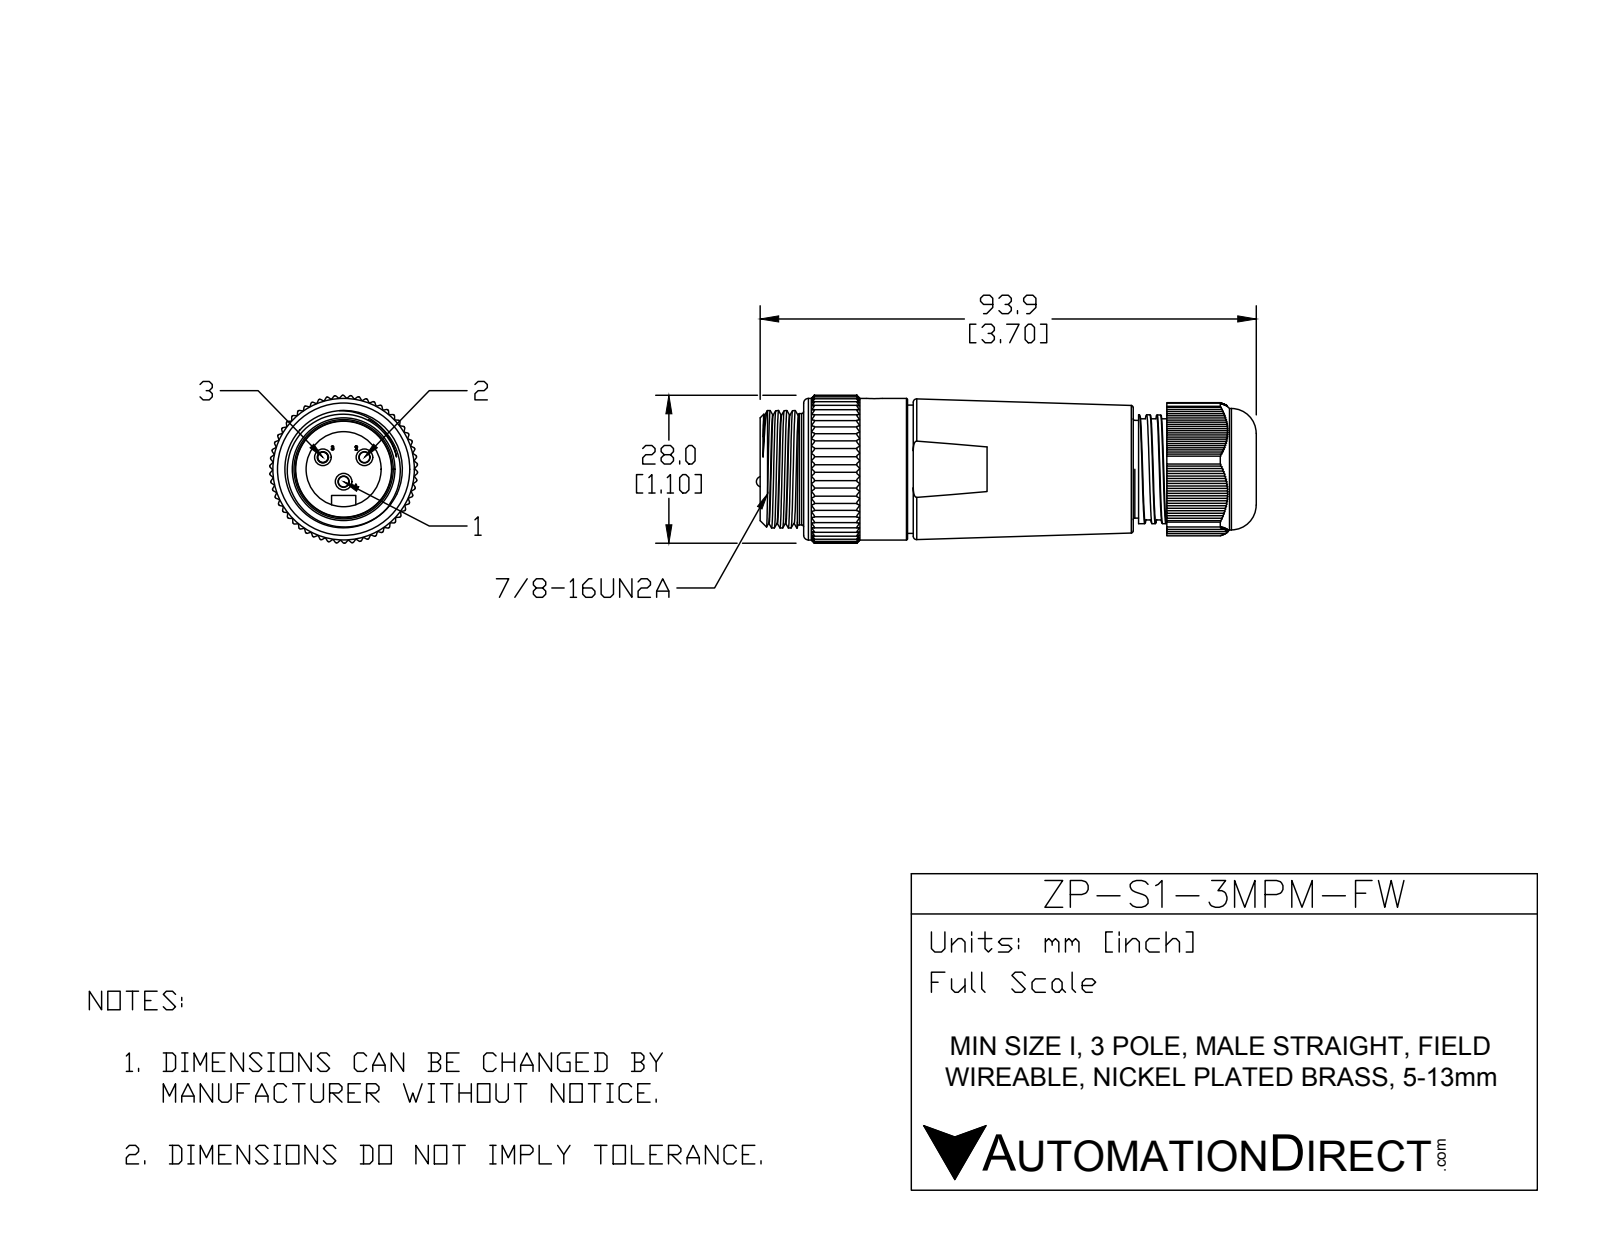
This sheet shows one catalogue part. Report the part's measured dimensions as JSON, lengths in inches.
{"part_name": "MIN-3MPM-FW", "step_written_by": "SolidWorks 2015 (AUTOMOTIVE_DESIGN)", "units": "inches", "bodies": {"solids": 1, "faces": 849, "planar": 449, "cylindrical": 328, "other": 72}, "overall_size": [3.726, 1.102, 1.102], "volume_in3": 2.637, "surface_area_in2": 19.59, "round_holes": [[0.138, 1], [0.53, 1], [0.56, 1], [0.72, 1], [1, 1]], "round_bosses_or_shafts": [[0.124, 3], [0.079, 3], [1.055, 1], [0.957, 1], [0.945, 1], [0.905, 1], [0.875, 1], [0.829, 1]], "partial_cylinders_radius": [[0.01, 116], [0.008, 58], [0.09, 1], [0.521, 1], [0.551, 1]], "face_to_face_distances": [0.014, 0.028, 0.043, 0.057, 2.747, 0.25, 0.754, 0.071, 0.58, 0.961]}
